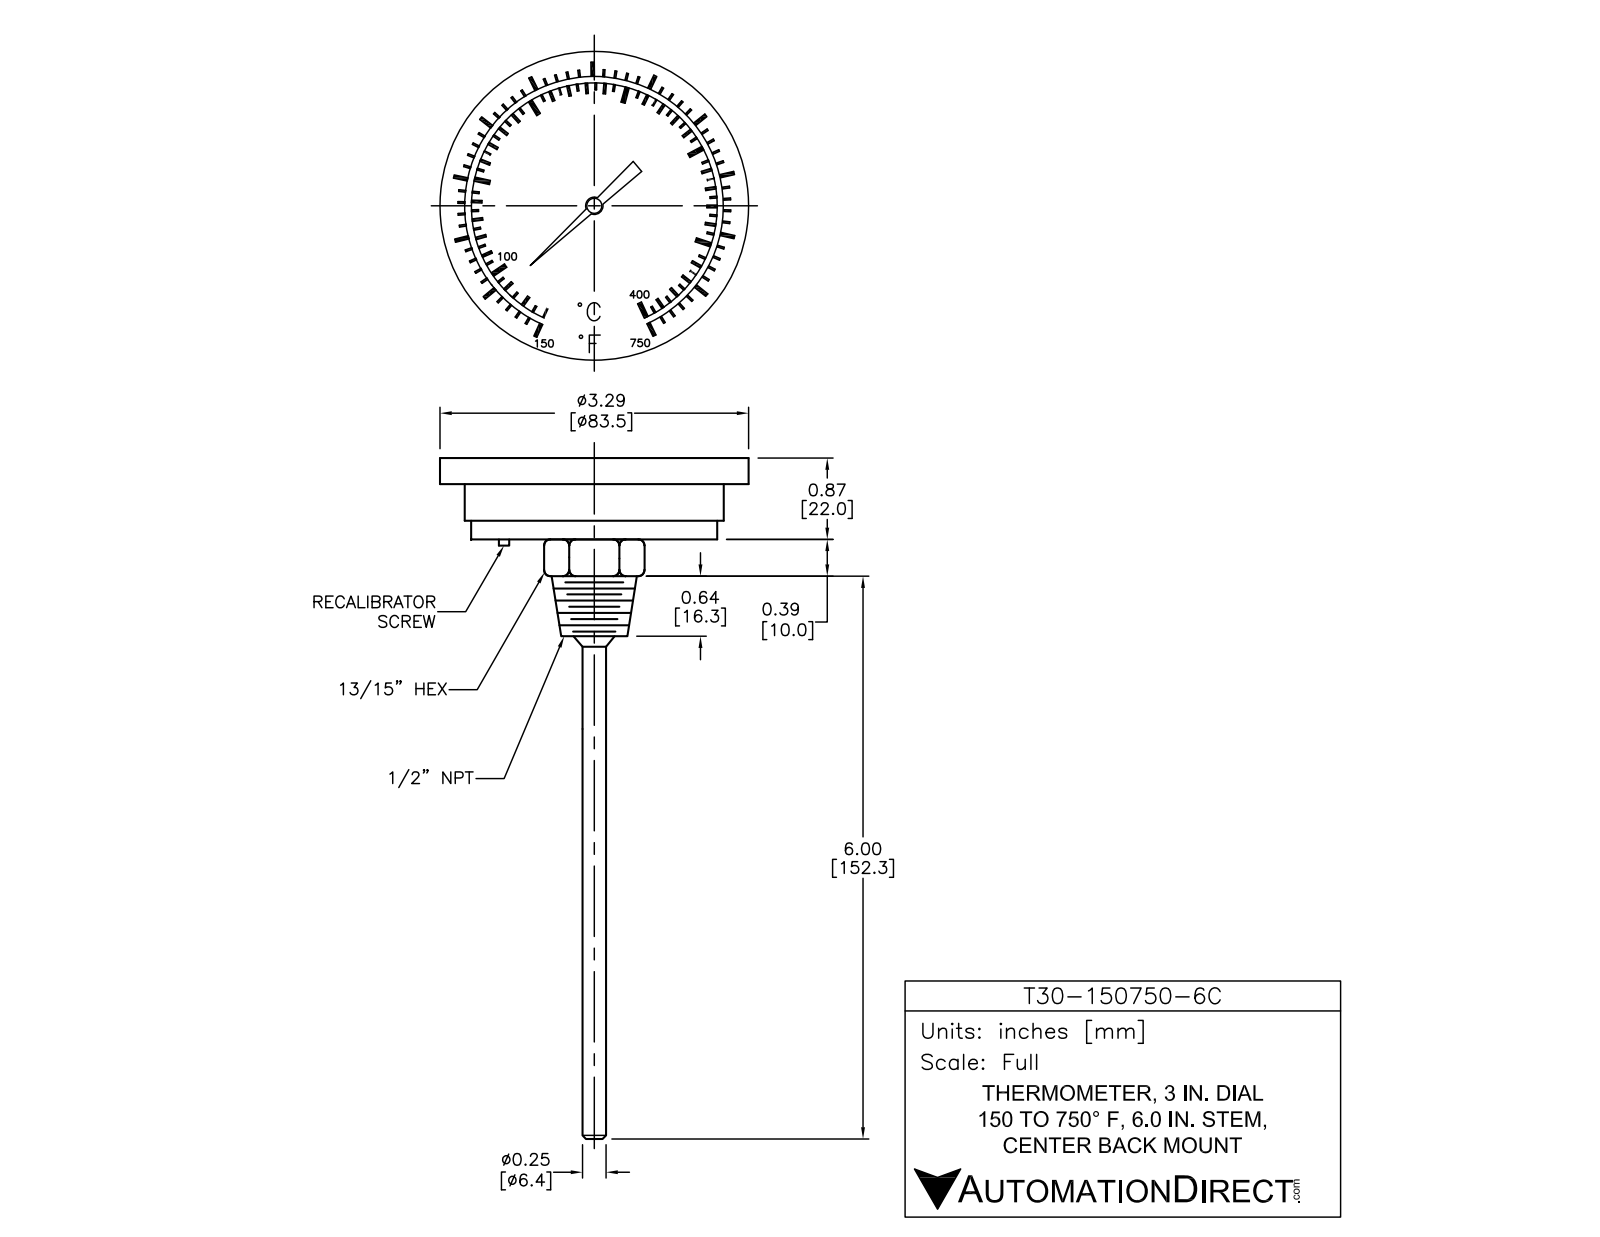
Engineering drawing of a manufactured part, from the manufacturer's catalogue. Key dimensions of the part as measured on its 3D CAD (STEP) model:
Part name (STEP PRODUCT): T30-150750-6C
STEP written by: SolidWorks 2021 (AUTOMOTIVE_DESIGN)
Units: inches
Bodies: 58 solids, 944 faces (735 planar, 124 cylindrical, 85 other)
Overall size (bounding box): 5.26 × 3.29 × 3.29
Volume: 3.15 in³ · Surface area: 34.1 in²
Round holes (diameter × count): ⌀0.067 ×1, ⌀2.69 ×1
Round bosses / shafts (diameter × count): ⌀3.29 ×1, ⌀2.76 ×1, ⌀2.62 ×1, ⌀0.845 ×1, ⌀0.258 ×1
Partial cylindrical surfaces — rounded edges, fillets, slot ends (radius × count): R0.04 ×1, R0.859 ×1, R0.969 ×1
Main face-to-face distances: 0.222, 0.078, 0.3, 0.87, 0.648, 0.57, 0.29, 0.59, 0.368, 0.28
